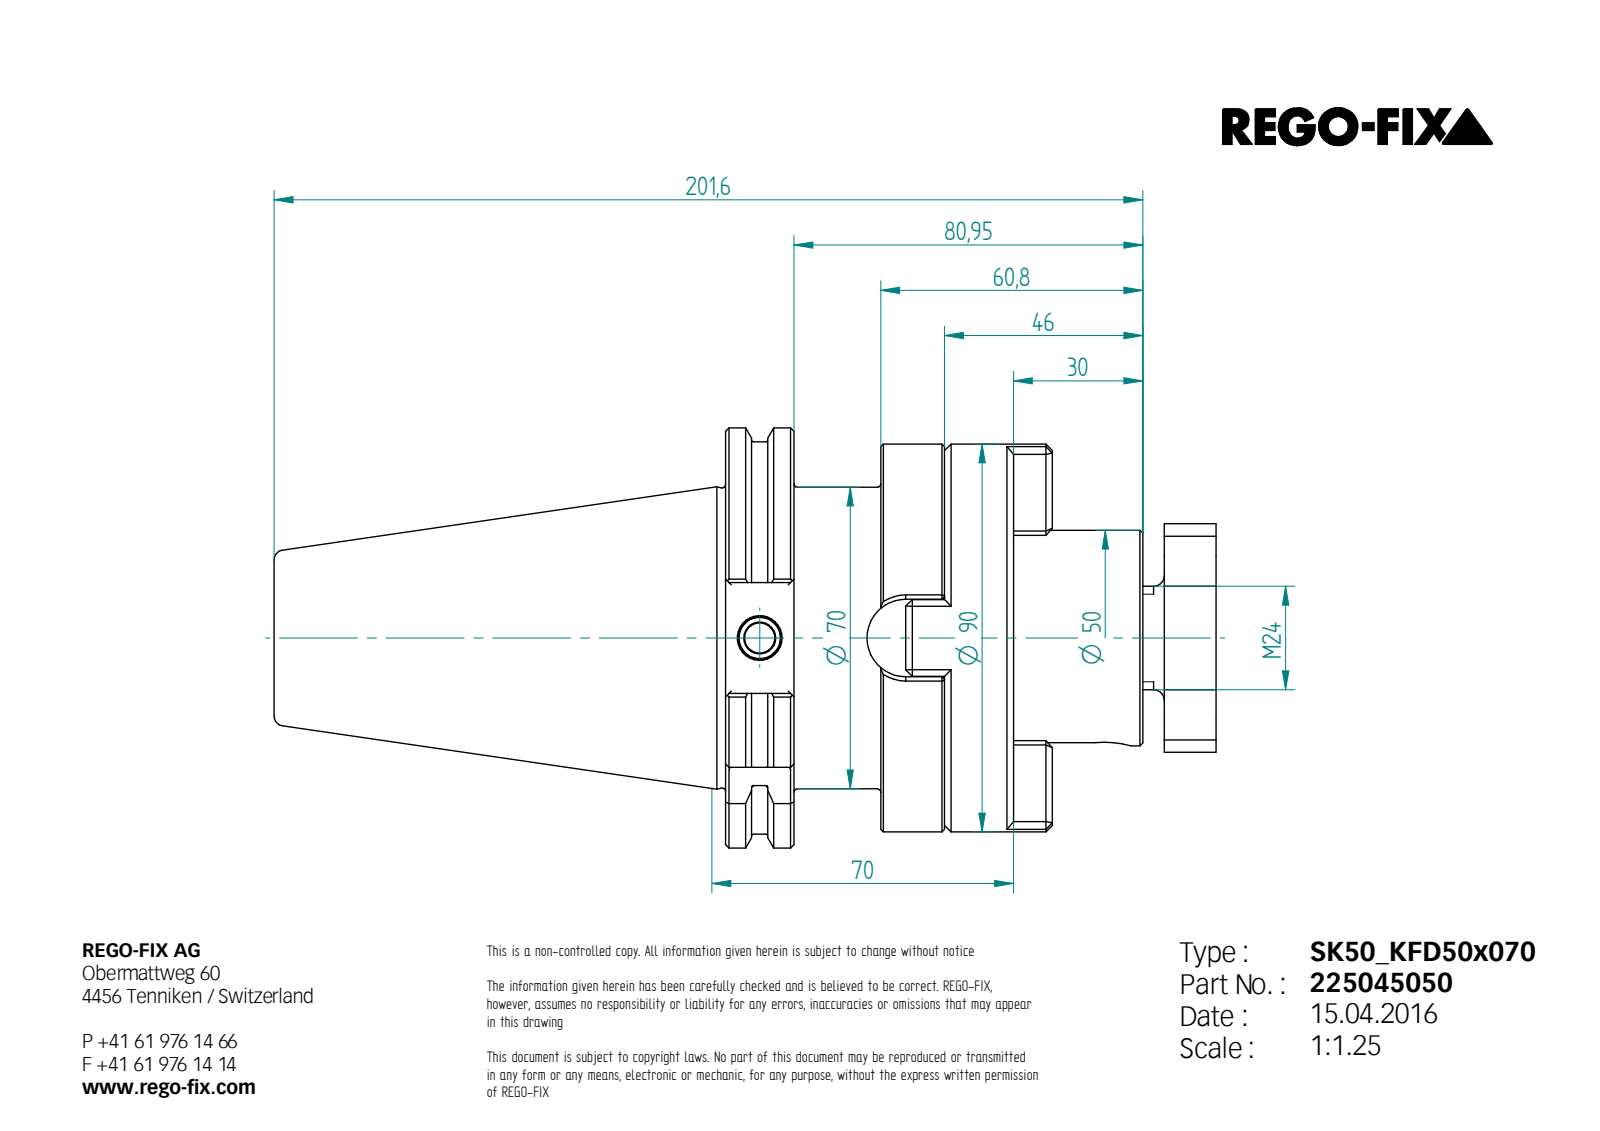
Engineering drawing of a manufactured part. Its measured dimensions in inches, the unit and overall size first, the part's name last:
Units: inches
Overall size (bounding box): 8.606 × 3.839 × 3.684
Round holes (diameter × count): ⌀0.276 ×1, ⌀0.394 ×1, ⌀0.817 ×1, ⌀0.984 ×1, ⌀1.969 ×1
Round bosses / shafts (diameter × count): ⌀3.583 ×1, ⌀3.543 ×1, ⌀2.756 ×1, ⌀1.945 ×1, ⌀0.945 ×1
Partial cylindrical surfaces — rounded edges, fillets, slot ends (radius × count): R0.02 ×5, R0.276 ×4, R0.236 ×2, R0.354 ×1, R1.043 ×1, R1.919 ×1
Main face-to-face distances: 0.63, 2, 2.63, 0.624, 1.376, 2.006, 1.417, 2.48, 0.793, 0.583
Volume: 40.41 in³ · Surface area: 148.3 in²
Bodies: 3 solids, 241 faces (133 planar, 41 cylindrical, 67 other)
STEP written by: Unknown (AUTOMOTIVE_DESIGN)
